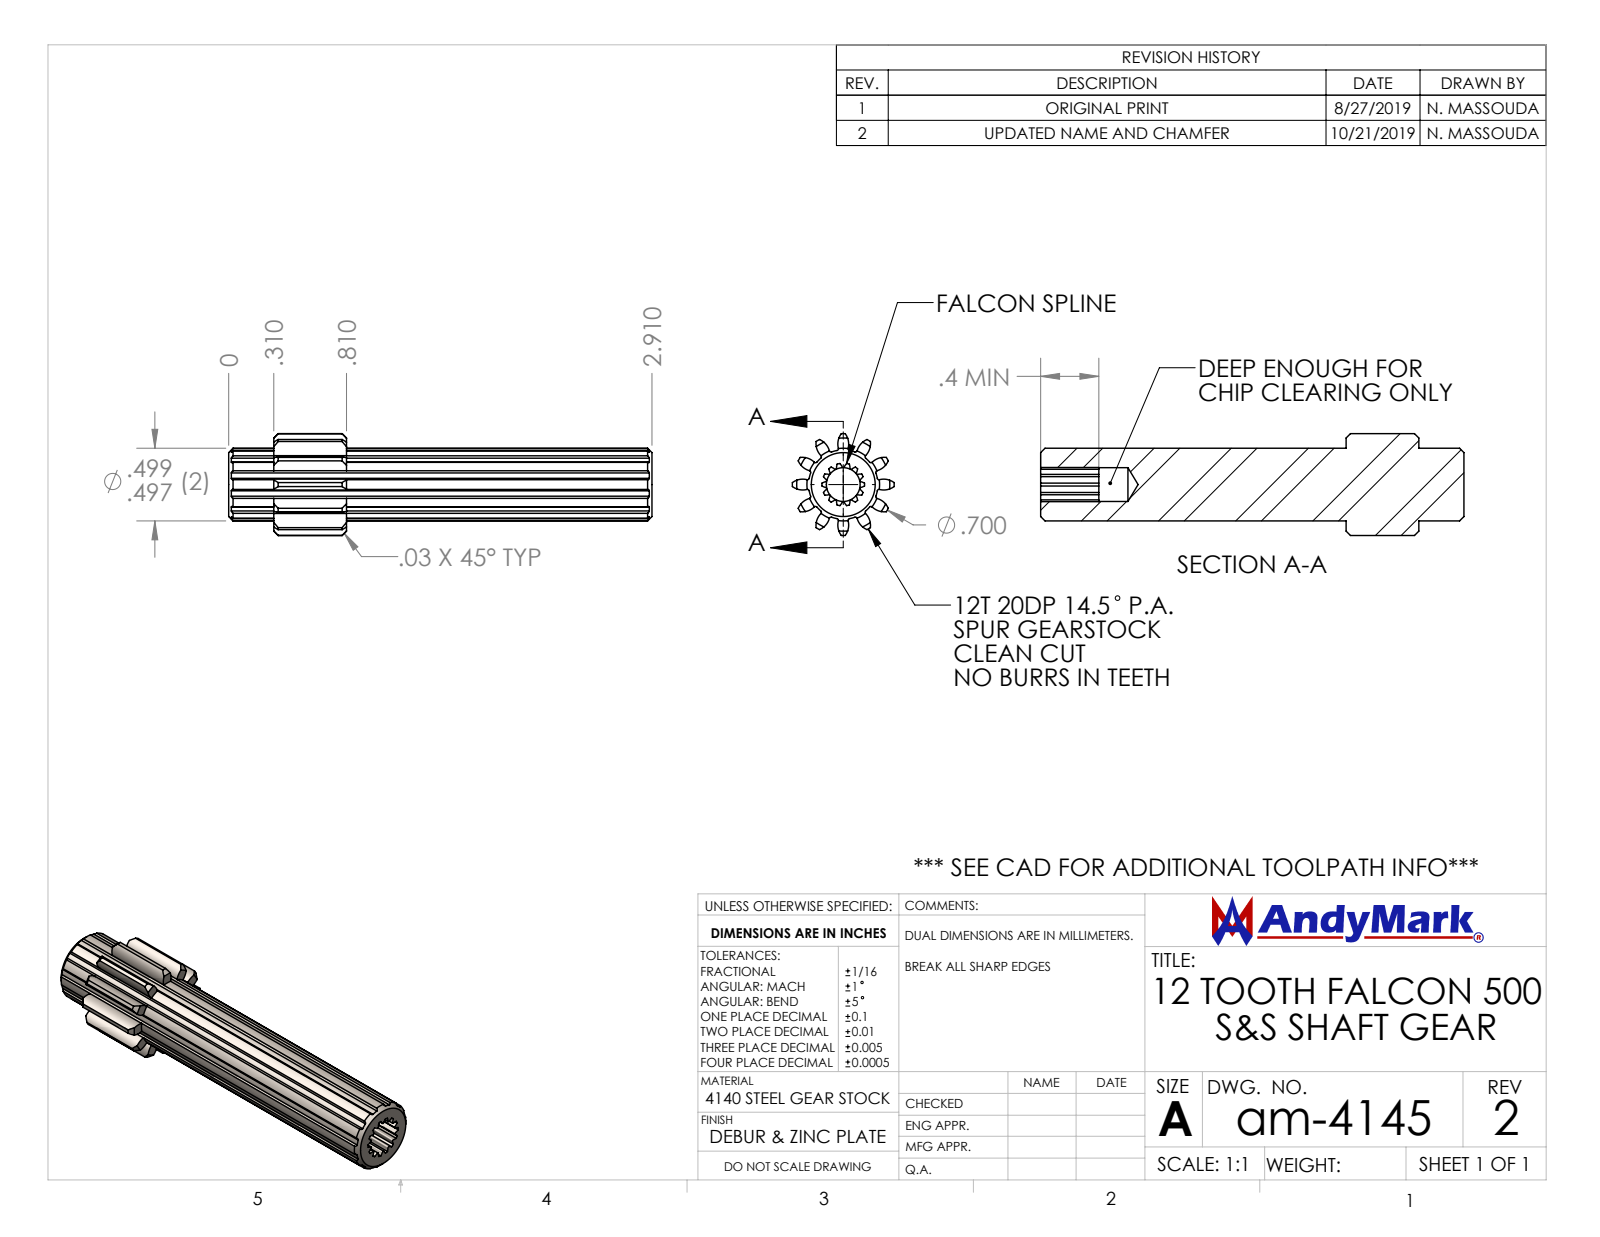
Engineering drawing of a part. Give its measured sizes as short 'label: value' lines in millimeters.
name: am-4145 12T Falcon 500 S&S Shaft Gear
written by: SolidWorks 2019 (CONFIG_CONTROL_DESIGN)
unit: mm
bodies: 1 solid, 197 faces (27 planar, 126 cylindrical, 44 other)
size: 73.9 × 17.8 × 17.8
volume: 9 030 mm³; area: 4 591 mm²
holes: 1× ⌀5.9
rounds: 24× R0.3, 24× R3, 1× R3.7, 1× R6, 1× R6.4, 1× R8.9
face distances: 73.9, 66, 7.9, 53.3, 12.7, 20.6, 10.2, 43.2, 55.9, 63.8
